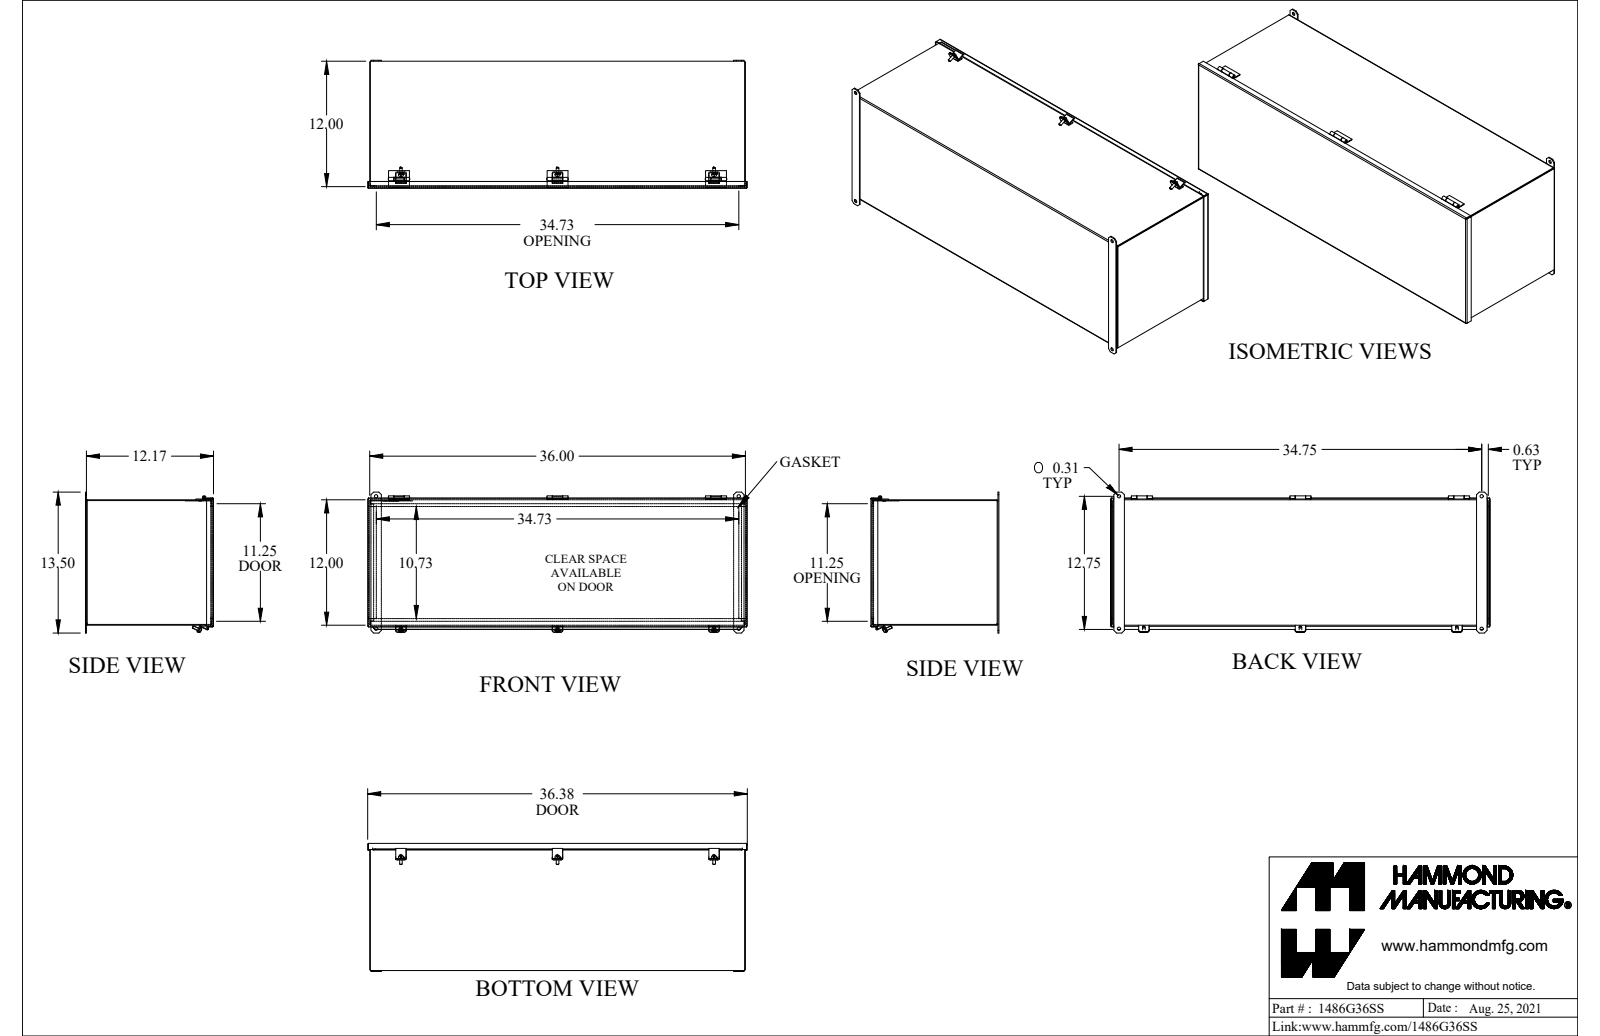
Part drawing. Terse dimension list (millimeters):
name: 1486G36
written by: SolidWorks 2021 (AUTOMOTIVE_DESIGN)
unit: mm
bodies: 12 solids, 485 faces (327 planar, 129 cylindrical, 29 other)
size: 923.9 × 342.9 × 311.6
volume: 2 720 000 mm³; area: 2 870 000 mm²
holes: 4× ⌀8, 3× ⌀5.4, 1× ⌀4.7
bosses: 3× ⌀12.2, 3× ⌀6.2, 1× ⌀8.6, 1× ⌀4.6
rounds: 8× R1, 8× R2.8, 6× R0.3, 6× R0.8, 6× R3.6, 6× R4.8, 5× R0.9, 5× R2.7
face distances: 1.8, 303, 1.8, 304.8, 301.2, 307.4, 305.6, 309.2, 307.3, 1.8
hole spacings: 322.3, 381, 882.7, 939.6, 762
